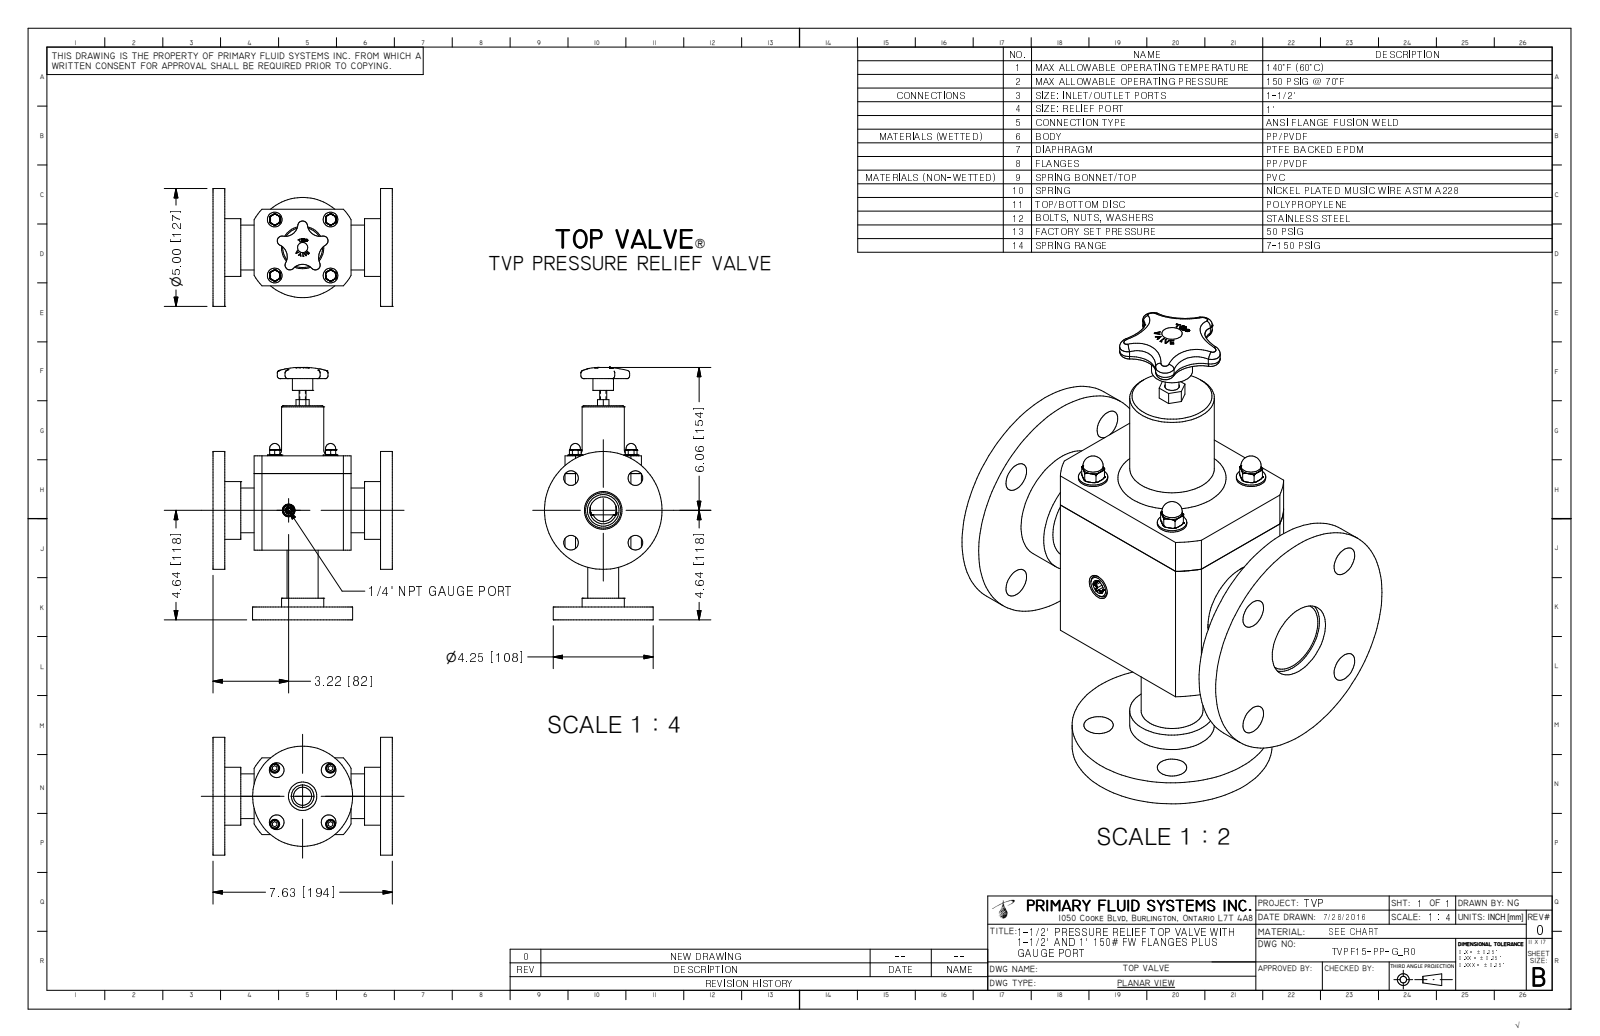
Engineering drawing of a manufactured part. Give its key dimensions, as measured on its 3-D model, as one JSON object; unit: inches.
{"part_name": "TVPF15-PP-G_R0", "step_written_by": "Autodesk Inventor 2009 (AUTOMOTIVE_DESIGN)", "units": "inches", "bodies": {"solids": 1, "faces": 398, "planar": 165, "cylindrical": 76, "other": 157}, "overall_size": [10.704, 7.625, 5], "volume_in3": 85.86, "surface_area_in2": 295.7, "round_holes": [[0.175, 4], [0.62, 4], [0.625, 4], [0.957, 1], [1.205, 1], [1.5, 1], [1.6, 1]], "round_bosses_or_shafts": [[0.625, 4], [0.433, 4], [0.375, 4], [5, 1], [4.25, 1], [2.45, 1], [1.9, 1], [1.8, 1]], "partial_cylinders_radius": [[0.027, 6], [0.085, 5], [0.205, 5], [0.536, 4], [0.656, 4], [0.625, 1], [0.745, 1], [2.375, 1]], "face_to_face_distances": [0.5, 7.125, 7.625, 6.625, 3.25, 1.75, 5.875, 1.25, 5.375, 2.954], "hole_center_spacings": [1.562, 1.937, 2.209, 2.294, 2.74, 0.117, 0.117, 1.679]}
